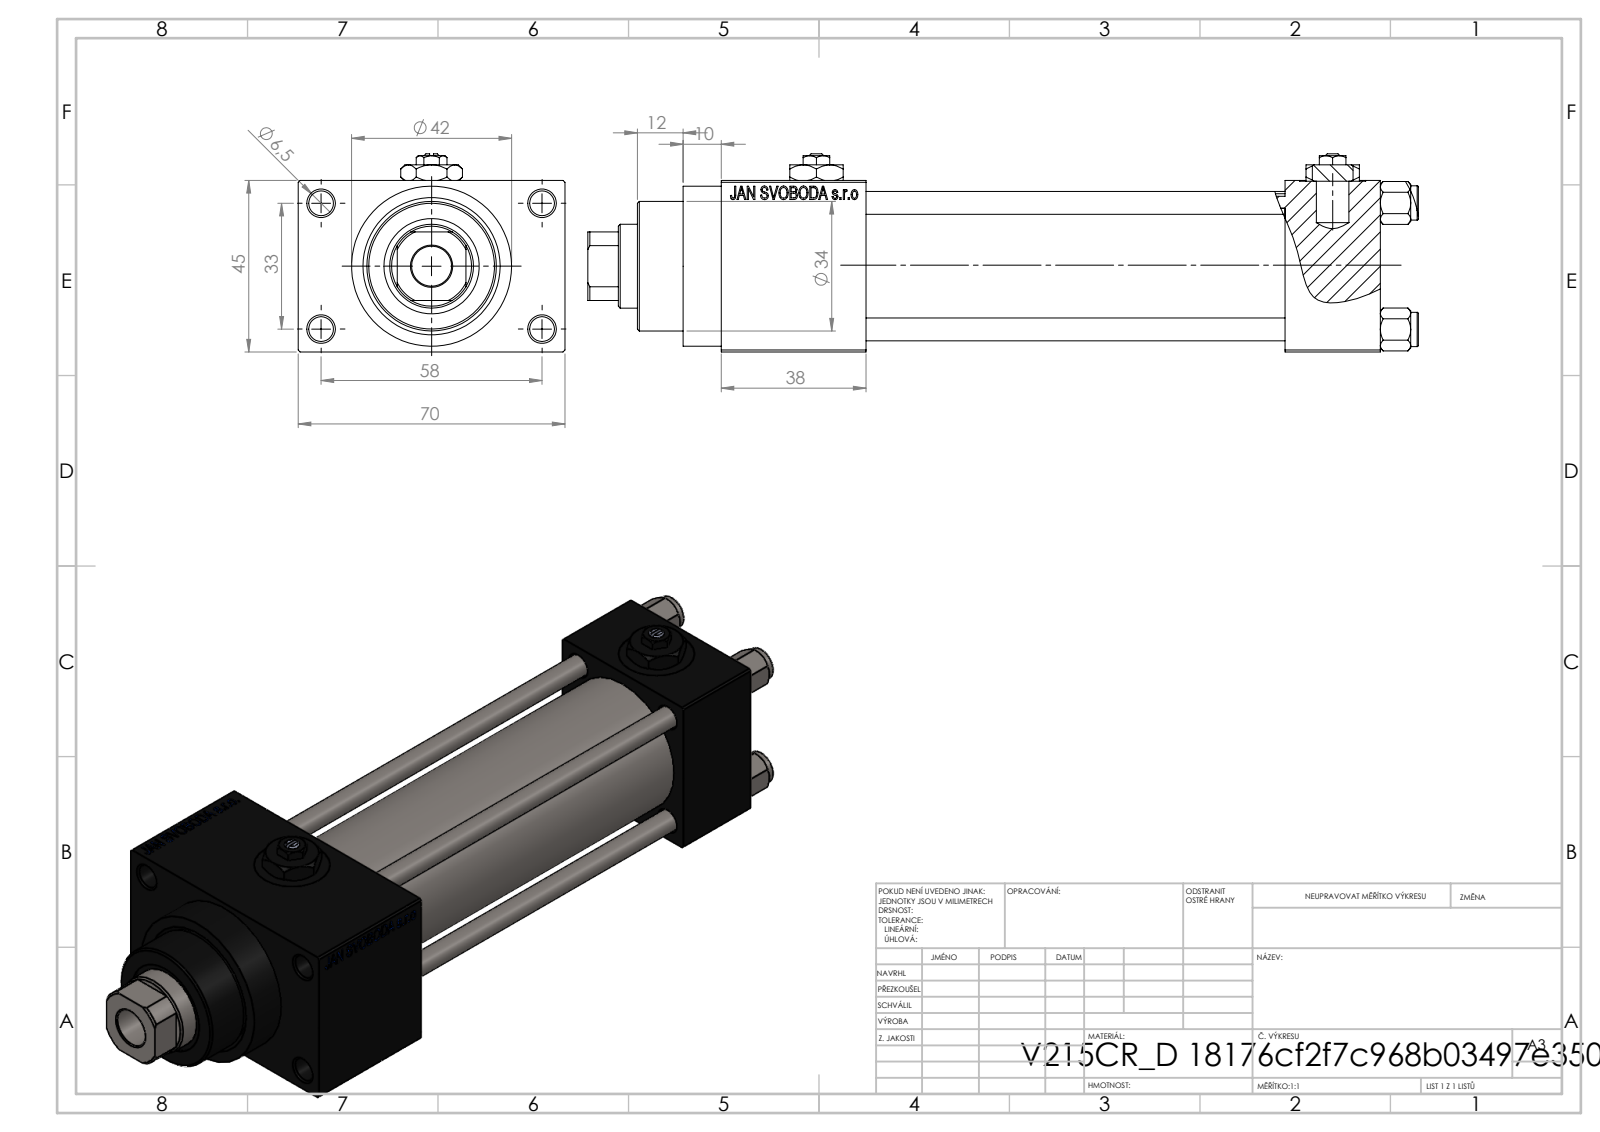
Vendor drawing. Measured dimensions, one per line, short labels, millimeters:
name: V215CR_D_Body; V215CR_D_TYCINKA; V215CR_VCP_D; V215_VC_A (+2 more)
written by: SolidWorks 2019 (CONFIG_CONTROL_DESIGN)
unit: mm
bodies: 13 solids, 1204 faces (542 planar, 100 cylindrical, 562 other)
size: 218 × 70 × 52
volume: 292 633 mm³; area: 102 977 mm²
holes: 4× ⌀6, 4× ⌀6.5, 2× ⌀7, 2× ⌀13.16, 2× ⌀20, 1× ⌀10.5, 1× ⌀22, 1× ⌀24, 1× ⌀25, 1× ⌀32, 1× ⌀33
bosses: 4× ⌀9, 1× ⌀42, 1× ⌀38, 1× ⌀34
rounds: 1× R10.5
face distances: 45, 25, 12.5, 57.5, 110, 135, 148, 38, 70, 173
hole spacings: 12.4, 23.48, 33.2, 33.37, 35.35, 45.6, 56.35, 33
